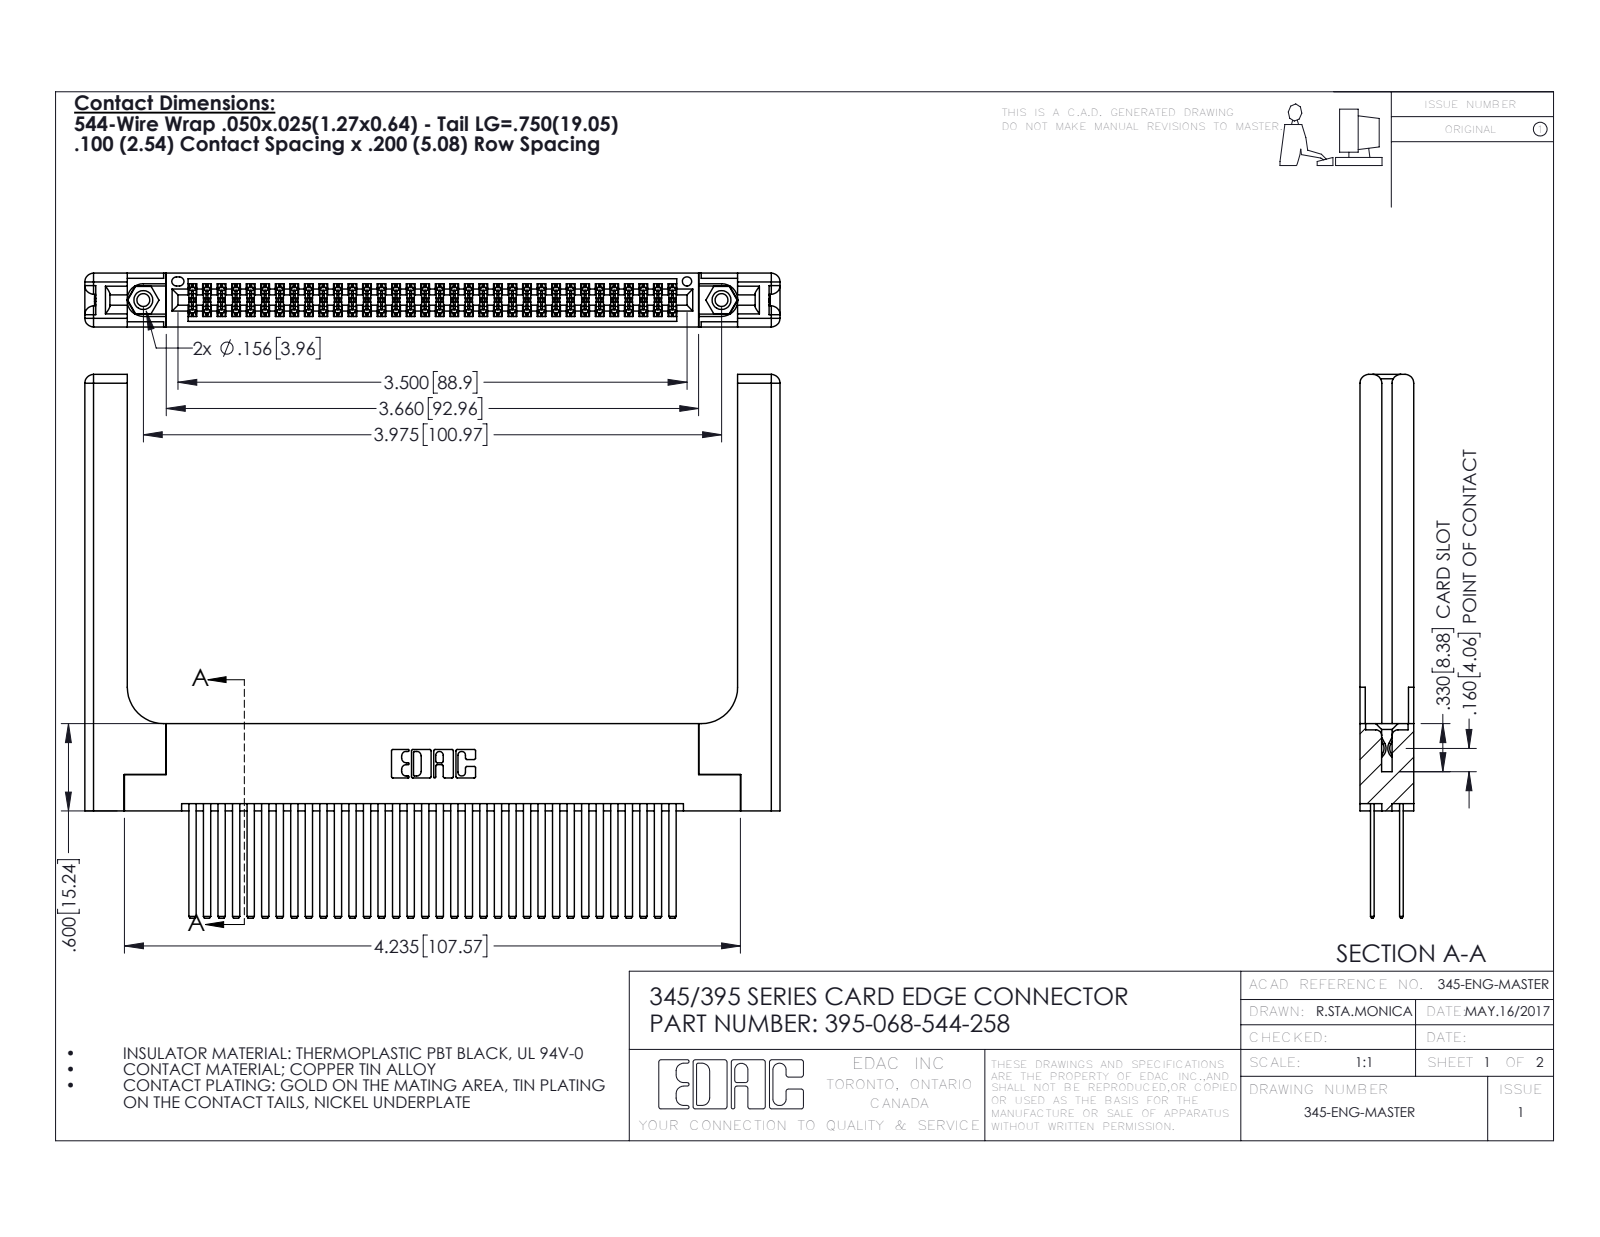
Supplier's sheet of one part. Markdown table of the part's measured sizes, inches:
| quantity | value |
| --- | --- |
| part name | 345-220-058_345-220-058; 345 Part_Flush Mounting Lugs - 0.156 Dia-TH; 395-068-544-258; 345-250-001_345-250-001-102 (+1 more) |
| STEP written by | SolidWorks 2016 (CONFIG_CONTROL_DESIGN) |
| units | inches |
| bodies | 73 solids, 3374 faces (2200 planar, 1114 cylindrical, 60 other) |
| overall size | 4.779 × 3.737 × 0.37 |
| volume | 1.29 in³ |
| surface area | 40.96 in² |
| round holes (diameter × count) | 0.089 × 2, 0.125 × 2, 0.156 × 2, 0.064 × 1 |
| round bosses / shafts (diameter × count) | 0.155 × 2 |
| partial cylindrical surfaces (radius × count) | 0.006 × 102, 0.01 × 22, 0.06 × 16, 0.007 × 6, 0.031 × 6, 0.026 × 3, 0.014 × 2, 0.019 × 2 |
| main face-to-face distances | 0.072, 0.298, 0.2, 0.098, 0.272, 0.025, 0.37, 0.225, 0.175, 0.148 |
| hole center spacings | 0.27, 3.74, 3.975 |
